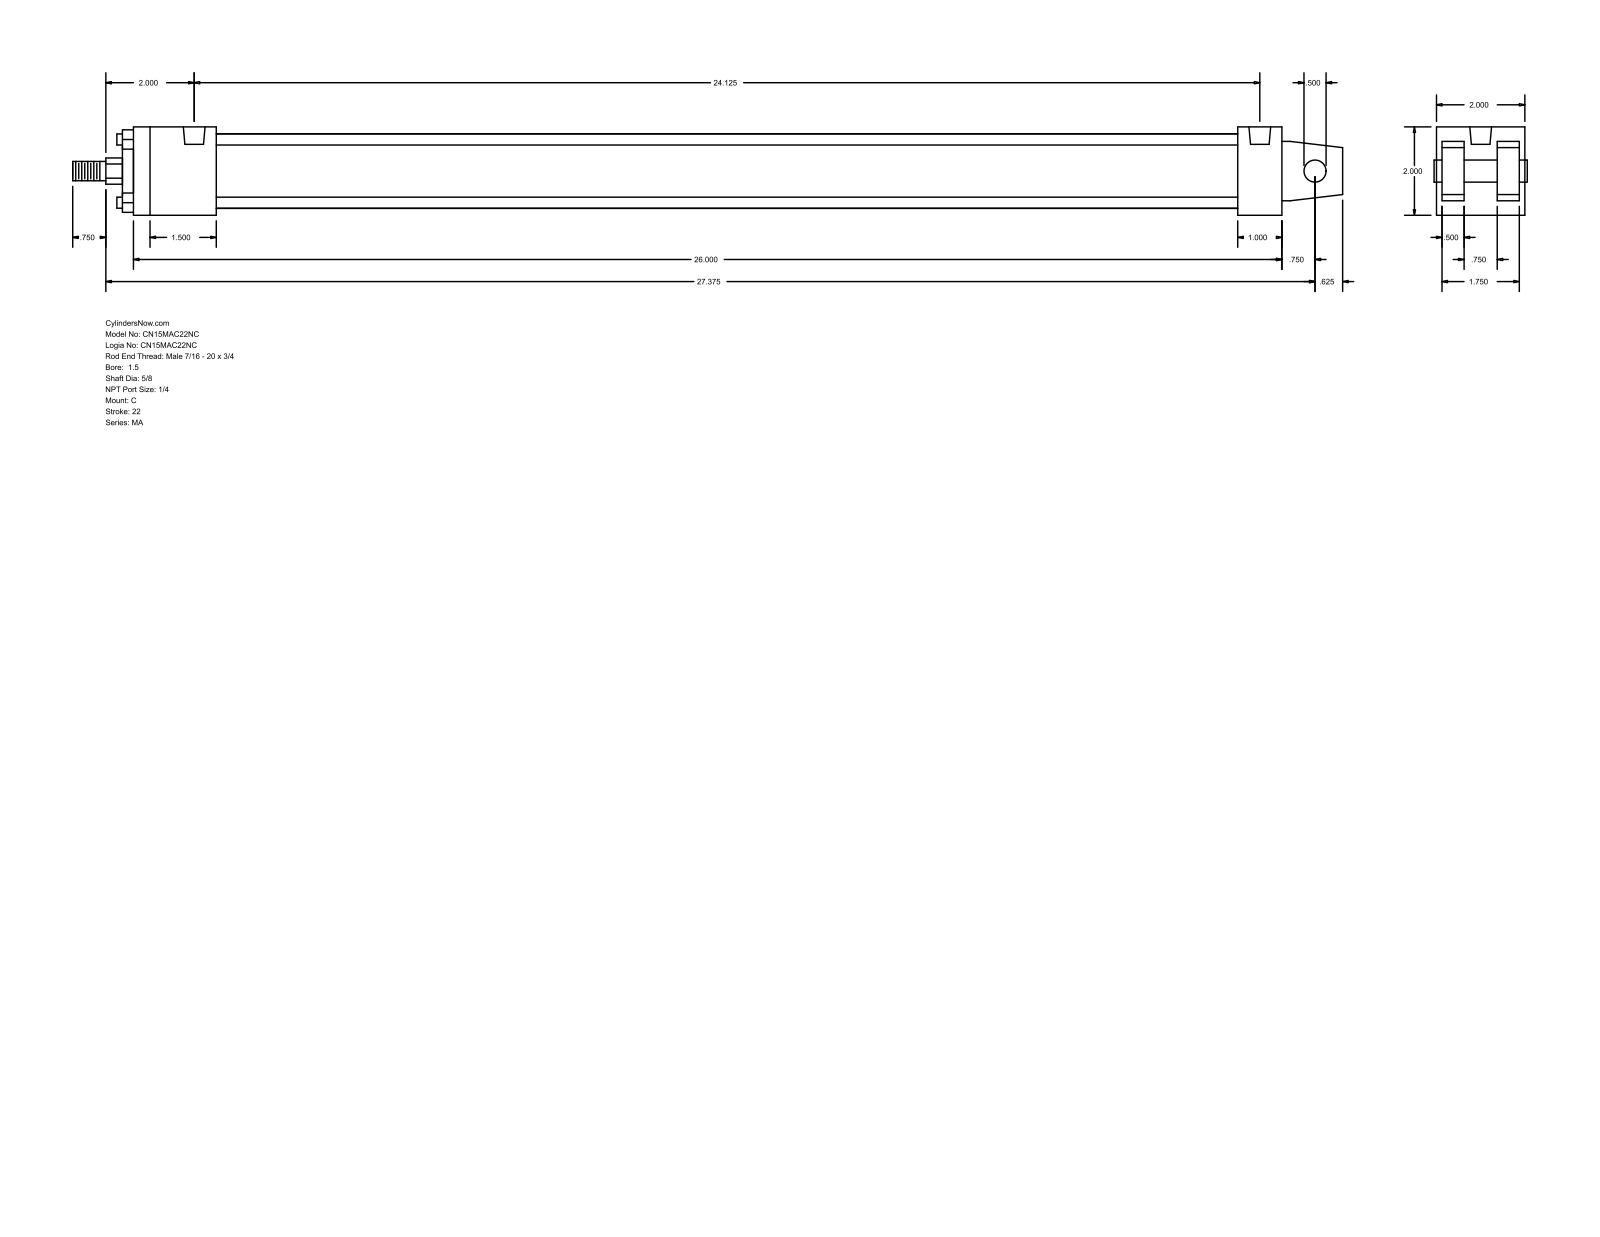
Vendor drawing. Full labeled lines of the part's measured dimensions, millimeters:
Part name (STEP PRODUCT): MA_C__0150_0.625
STEP written by: GSSL Pune (CONFIG_CONTROL_DESIGN)
Units: millimetres
Bodies: 0 solids, 103 faces (76 planar, 27 cylindrical, 0 other)
Overall size (bounding box): 730.25 × 50.8 × 50.8
Round holes (diameter × count): ⌀7.94 ×4, ⌀12.49 ×2
Round bosses / shafts (diameter × count): ⌀6.35 ×4, ⌀42.93 ×1, ⌀28.57 ×1, ⌀15.88 ×1, ⌀12.7 ×1, ⌀11.11 ×1
Partial cylindrical surfaces — rounded edges, fillets, slot ends (radius × count): R7.54 ×1
Main face-to-face distances: 50.8, 34.93, 12.7, 15.87, 3.17, 47.63, 31.76, 660.39, 635, 25.39
Hole centre spacings: 612.78
